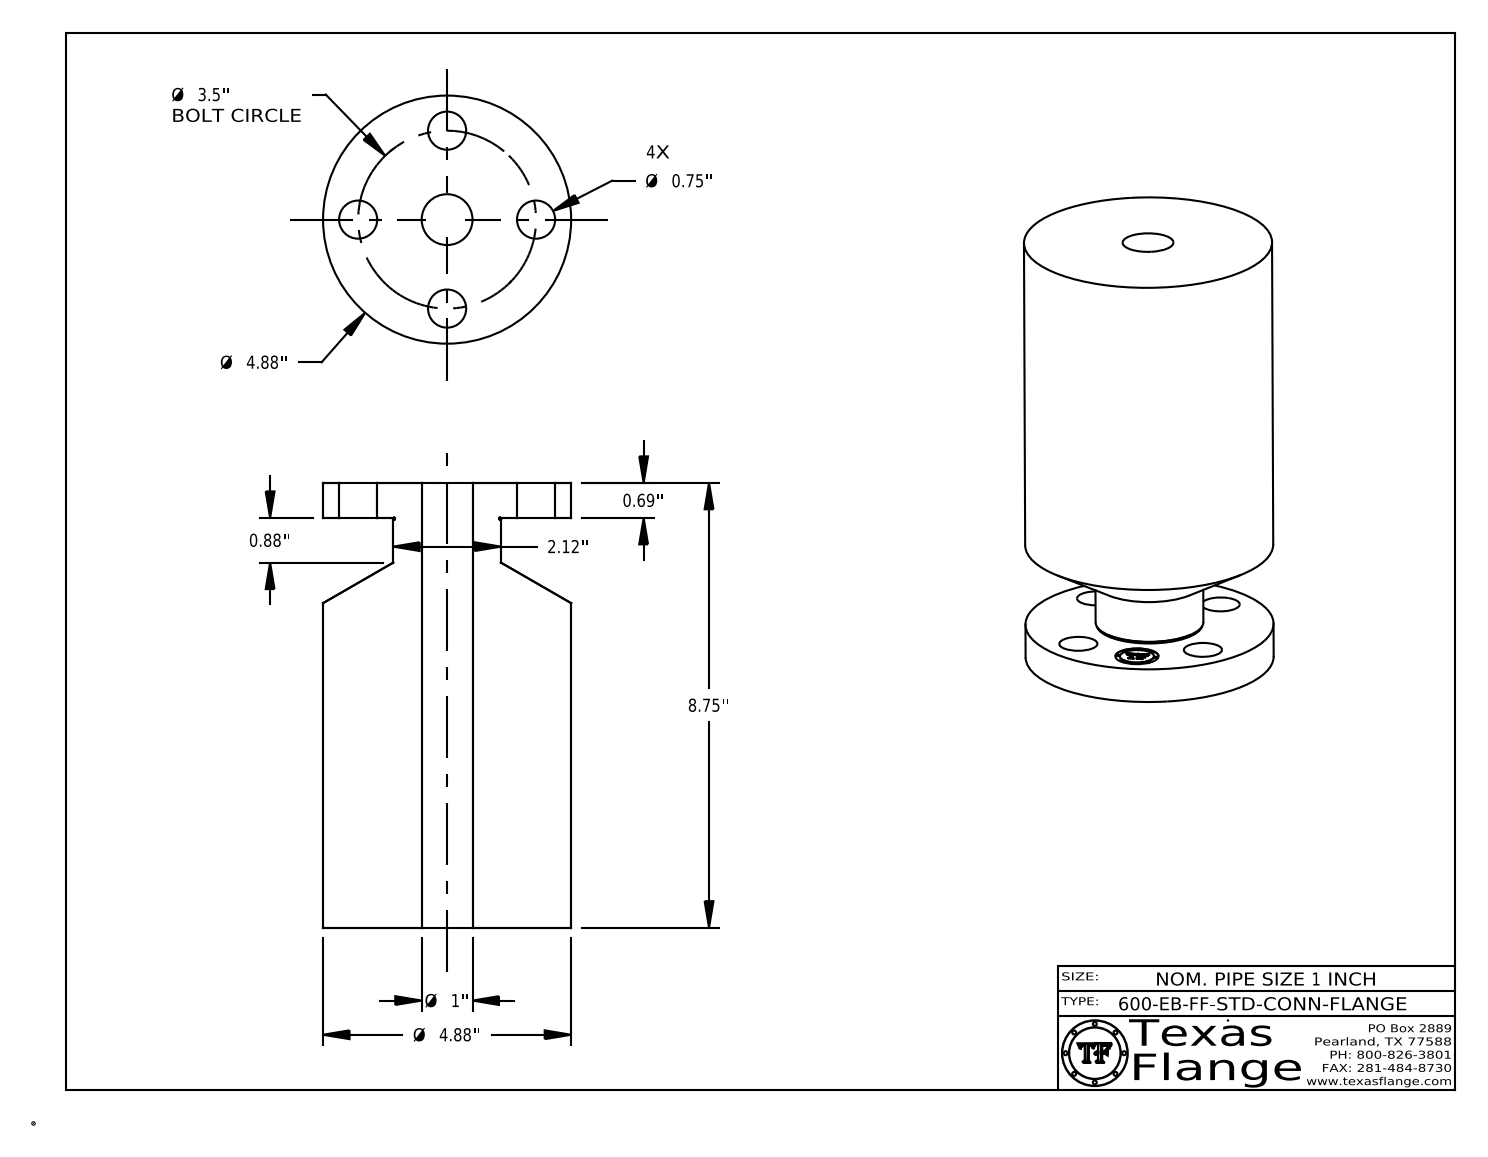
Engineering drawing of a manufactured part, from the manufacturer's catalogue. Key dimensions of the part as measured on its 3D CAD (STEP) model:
Part name (STEP PRODUCT): 1-600-EB-FF-STD-CONN-FLANGE
STEP written by: CATIA V5 STEP AP214 (AUTOMOTIVE_DESIGN)
Units: inches
Bodies: 1 solid, 410 faces (368 planar, 36 cylindrical, 6 other)
Overall size (bounding box): 8.75 × 4.88 × 4.88
Volume: 135.4 in³ · Surface area: 213.6 in²
Round holes (diameter × count): ⌀0.75 ×4, ⌀0.85 ×1, ⌀1 ×1
Round bosses / shafts (diameter × count): ⌀0.051 ×8, ⌀4.88 ×1, ⌀2.12 ×1, ⌀0.67 ×1
Main face-to-face distances: 8.75, 0.69, 8.06, 0.685, 8.065, 0.016, 0.254, 0.249, 0.046, 0.165
Hole centre spacings: 1.75, 2.475, 1.339, 3.233, 3.5
